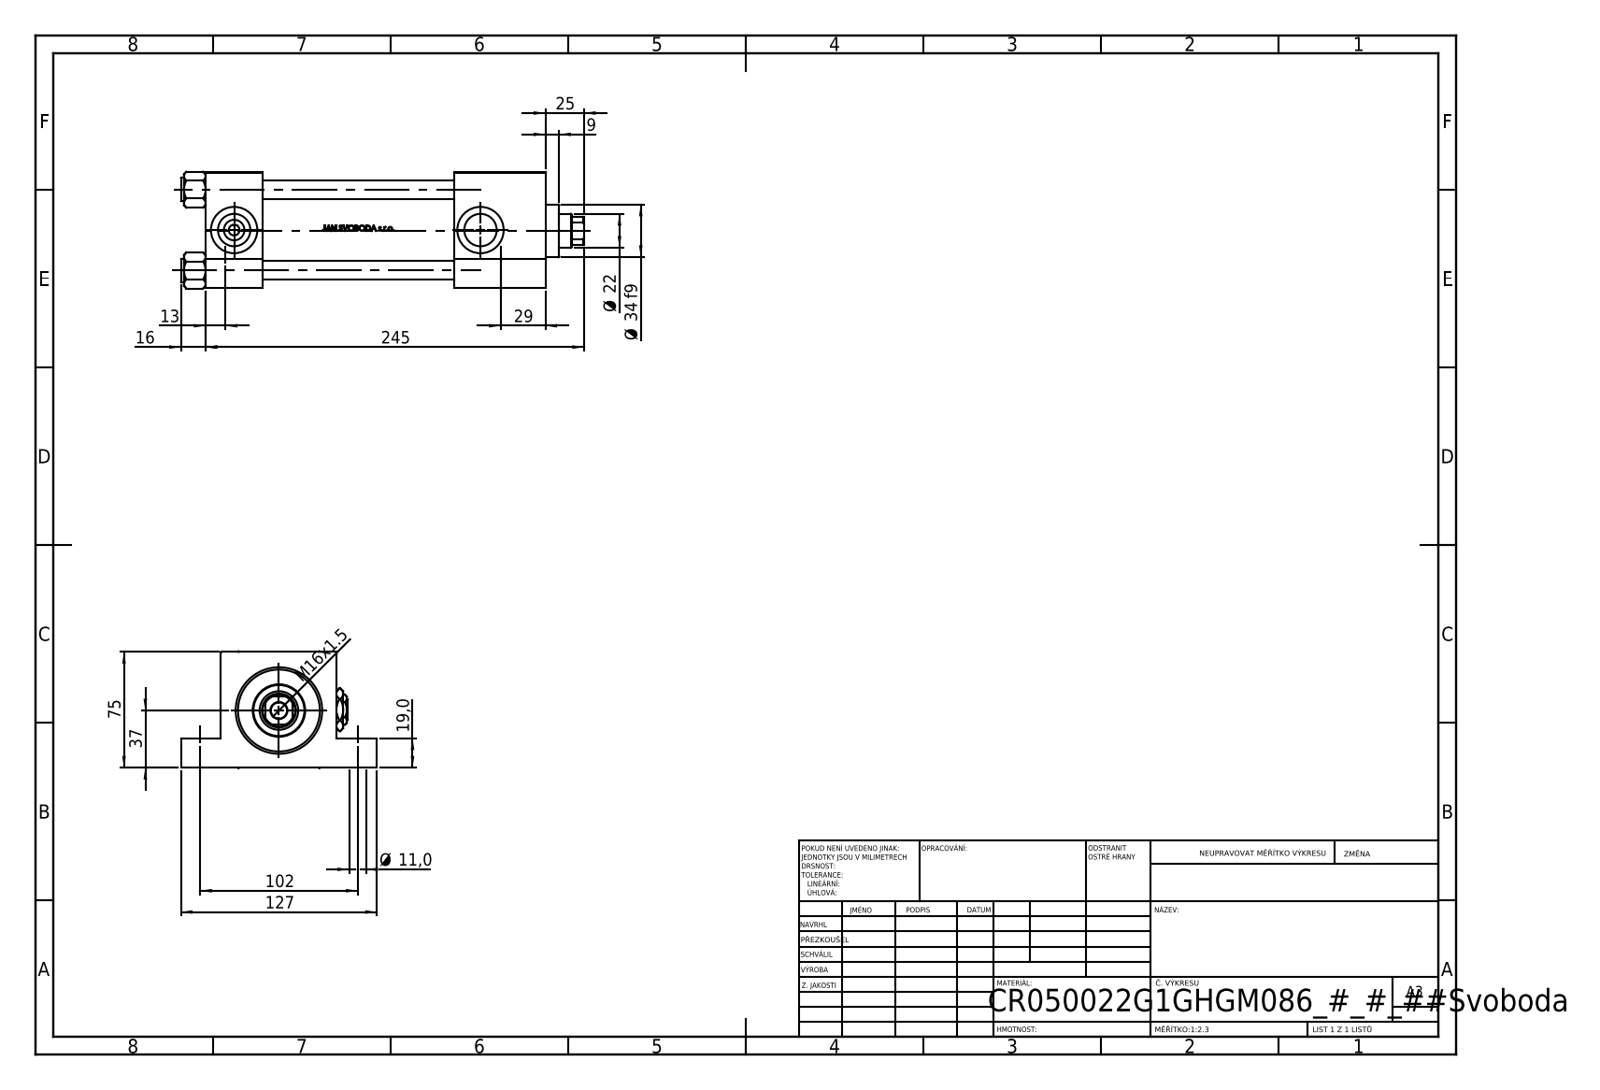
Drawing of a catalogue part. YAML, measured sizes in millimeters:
part_name: "NUT_M5_G; Zatka_pro_OIL_PORT; V215CR_G_Body; V215CR_VCP_G (+2 more)"
step_written_by: "SolidWorks 2019 (CONFIG_CONTROL_DESIGN)"
units: millimeters
bodies: {solids: 12, faces: 1134, planar: 454, cylindrical: 128, other: 552}
overall_size: [261, 127, 75.54]
volume: 840317
surface_area: 197796
round_holes:
  - {diameter: 11, count: 4}
  - {diameter: 12, count: 4}
  - {diameter: 7, count: 2}
  - {diameter: 20.96, count: 2}
  - {diameter: 30, count: 2}
  - {diameter: 10.5, count: 1}
  - {diameter: 22, count: 1}
  - {diameter: 25, count: 1}
  - {diameter: 41, count: 1}
  - {diameter: 50, count: 1}
  - {diameter: 53, count: 1}
round_bosses_or_shafts:
  - {diameter: 15, count: 4}
  - {diameter: 56, count: 1}
  - {diameter: 34, count: 1}
partial_cylinders:
  - {radius: 10.5, count: 1}
face_to_face_distances: [75, 37, 220, 183, 19, 56, 161, 124, 59, 26]
hole_center_spacings: [52.3, 36.63, 37.34, 73.96, 102, 178, 205.15, 159.5]
